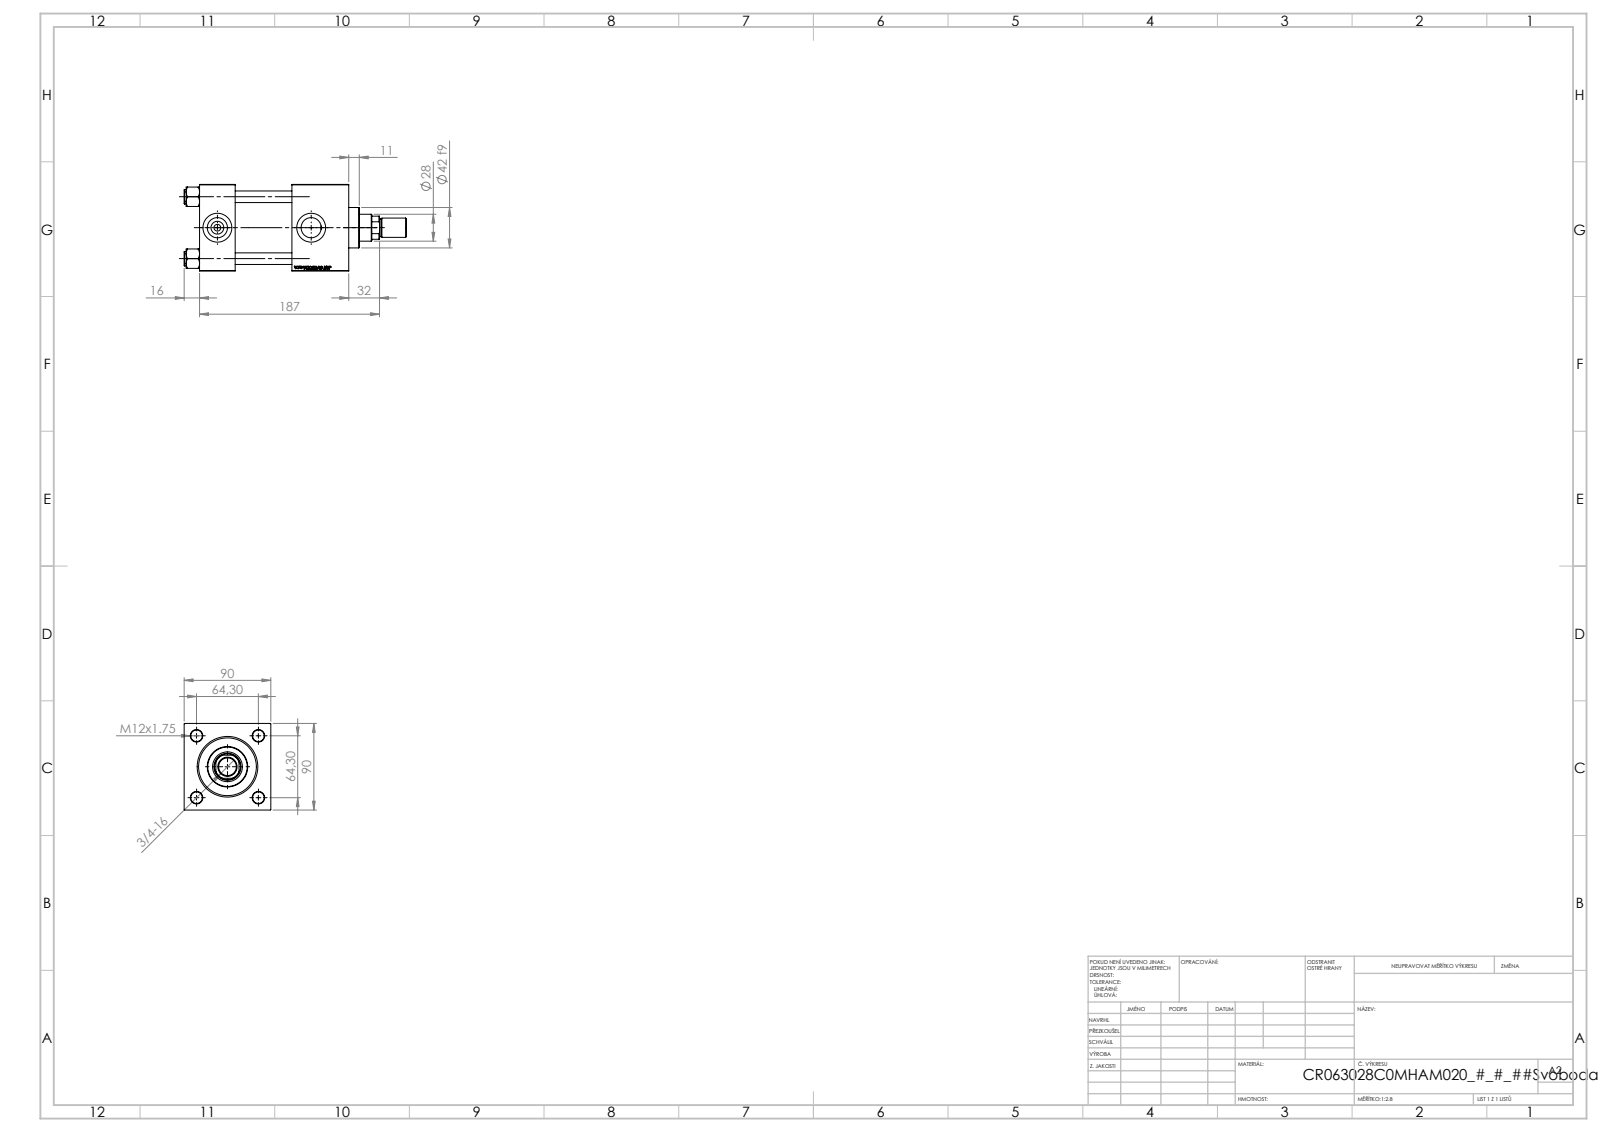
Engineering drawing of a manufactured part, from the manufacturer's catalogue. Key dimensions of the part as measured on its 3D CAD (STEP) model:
Part name (STEP PRODUCT): NUT_M5_C; V215CR_VCP_C; V215_VC_A; ROD_END_AH (+2 more)
STEP written by: SolidWorks 2019 (CONFIG_CONTROL_DESIGN)
Units: millimetres
Bodies: 12 solids, 1162 faces (530 planar, 90 cylindrical, 542 other)
Overall size (bounding box): 231 × 90 × 90
Volume: 955 538 mm³ · Surface area: 181 562 mm²
Round holes (diameter × count): ⌀12 ×4, ⌀7 ×2, ⌀20.96 ×2, ⌀30 ×2, ⌀18.5 ×1, ⌀28 ×1, ⌀31 ×1, ⌀50 ×1, ⌀60 ×1, ⌀63 ×1
Round bosses / shafts (diameter × count): ⌀15 ×4, ⌀69 ×1, ⌀42 ×1, ⌀20 ×1, ⌀18 ×1
Partial cylindrical surfaces — rounded edges, fillets, slot ends (radius × count): R13.5 ×1
Main face-to-face distances: 90, 59, 37, 155, 118, 96, 126.3, 89.3, 30.3, 28.7
Hole centre spacings: 45.47, 64.3, 90.93, 97.5
